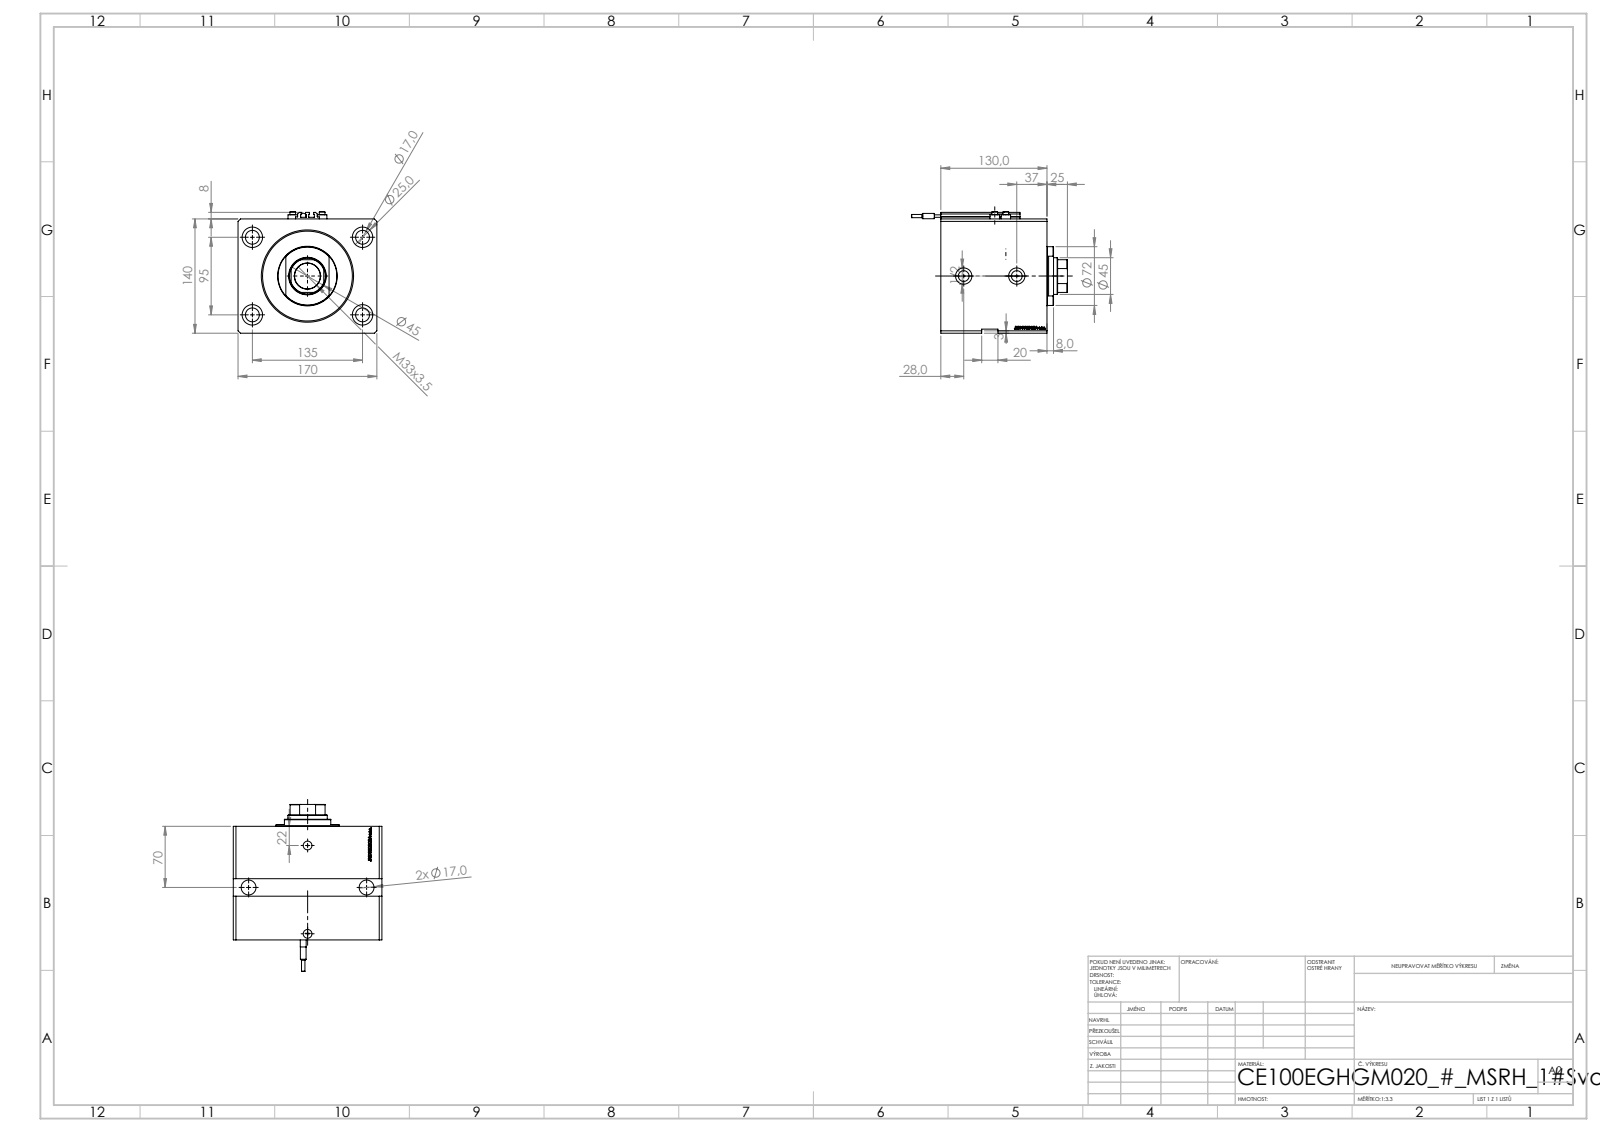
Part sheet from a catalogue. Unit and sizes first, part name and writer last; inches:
Units: inches
Overall size (bounding box): 7.52 × 6.693 × 5.866
Round holes (diameter × count): ⌀0.669 ×6, ⌀0.049 ×4, ⌀0.157 ×4, ⌀0.984 ×4, ⌀0.394 ×2, ⌀0.518 ×2, ⌀0.787 ×2, ⌀1.24 ×1, ⌀1.772 ×1, ⌀3.937 ×1, ⌀4.449 ×1
Round bosses / shafts (diameter × count): ⌀0.457 ×4, ⌀0.276 ×4, ⌀2.835 ×1, ⌀0.268 ×1, ⌀0.256 ×1, ⌀0.157 ×1
Partial cylindrical surfaces — rounded edges, fillets, slot ends (radius × count): R0.008 ×10, R0.866 ×1
Main face-to-face distances: 5.512, 5.118, 6.693, 1.138, 3.98, 0.984, 4.134, 2.996, 0.787, 3.346
Hole centre spacings: 3.25, 5.315, 0.535, 1.324, 1.417, 1.515, 1.799, 1.963
Volume: 169.6 in³ · Surface area: 456.4 in²
Bodies: 9 solids, 1129 faces (563 planar, 124 cylindrical, 442 other)
Part name (STEP PRODUCT): V250CE_C_VCP; SWITCH_V250CE; V250CE_E_Body; V250CE_VC_E (+1 more)
STEP written by: SolidWorks 2019 (CONFIG_CONTROL_DESIGN)
